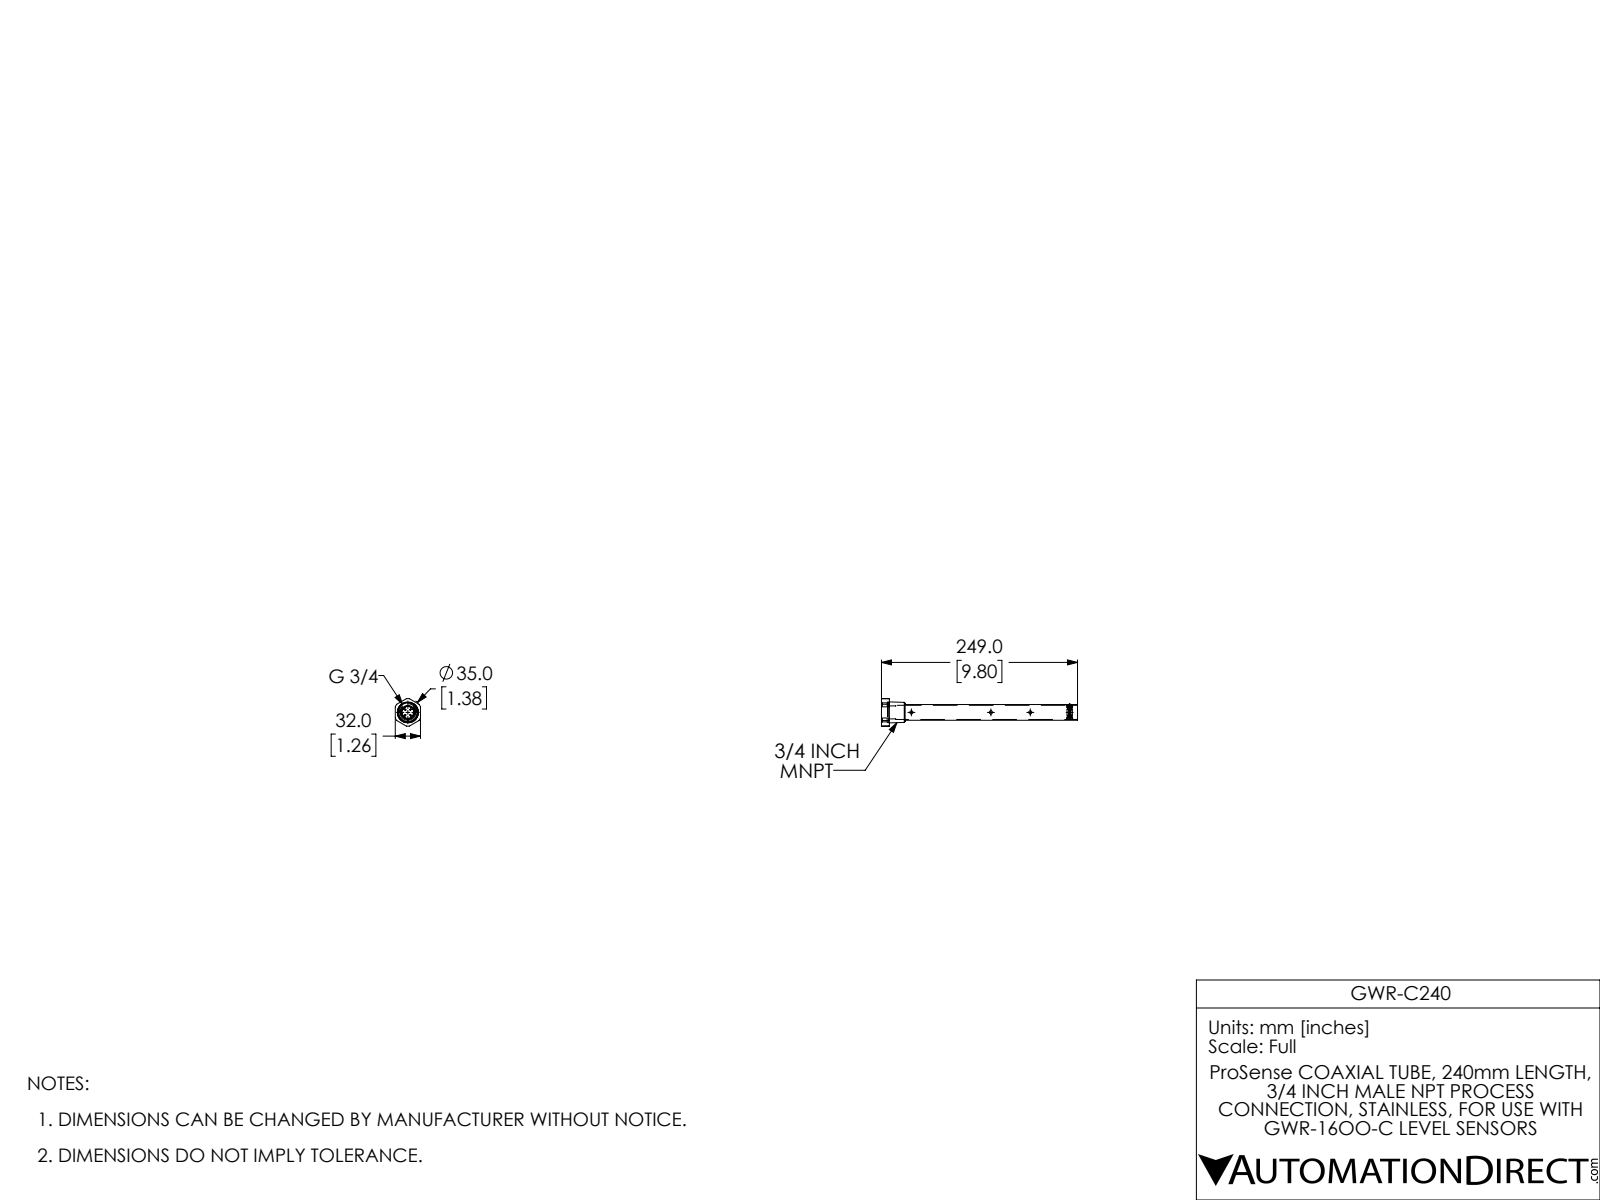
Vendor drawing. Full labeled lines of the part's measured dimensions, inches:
Part name (STEP PRODUCT): GWR-C240
STEP written by: SolidWorks 2017 (AUTOMOTIVE_DESIGN)
Units: inches
Bodies: 1 solid, 134 faces (32 planar, 78 cylindrical, 24 other)
Overall size (bounding box): 9.803 × 1.378 × 1.26
Volume: 1.442 in³ · Surface area: 51.18 in²
Round holes (diameter × count): ⌀0.157 ×4, ⌀0.591 ×1, ⌀0.65 ×1, ⌀0.709 ×1, ⌀0.95 ×1
Round bosses / shafts (diameter × count): ⌀0.039 ×2, ⌀0.787 ×1, ⌀0.689 ×1
Partial cylindrical surfaces — rounded edges, fillets, slot ends (radius × count): R0.008 ×8, R0.075 ×8, R0.159 ×1, R0.384 ×1, R0.689 ×1
Main face-to-face distances: 1.26, 0.354, 0.394, 0.039, 0.787, 0.827, 1.181, 0.125, 0.17, 8.206
Hole centre spacings: 1.969, 3.937, 3.976, 5.945, 7.913
